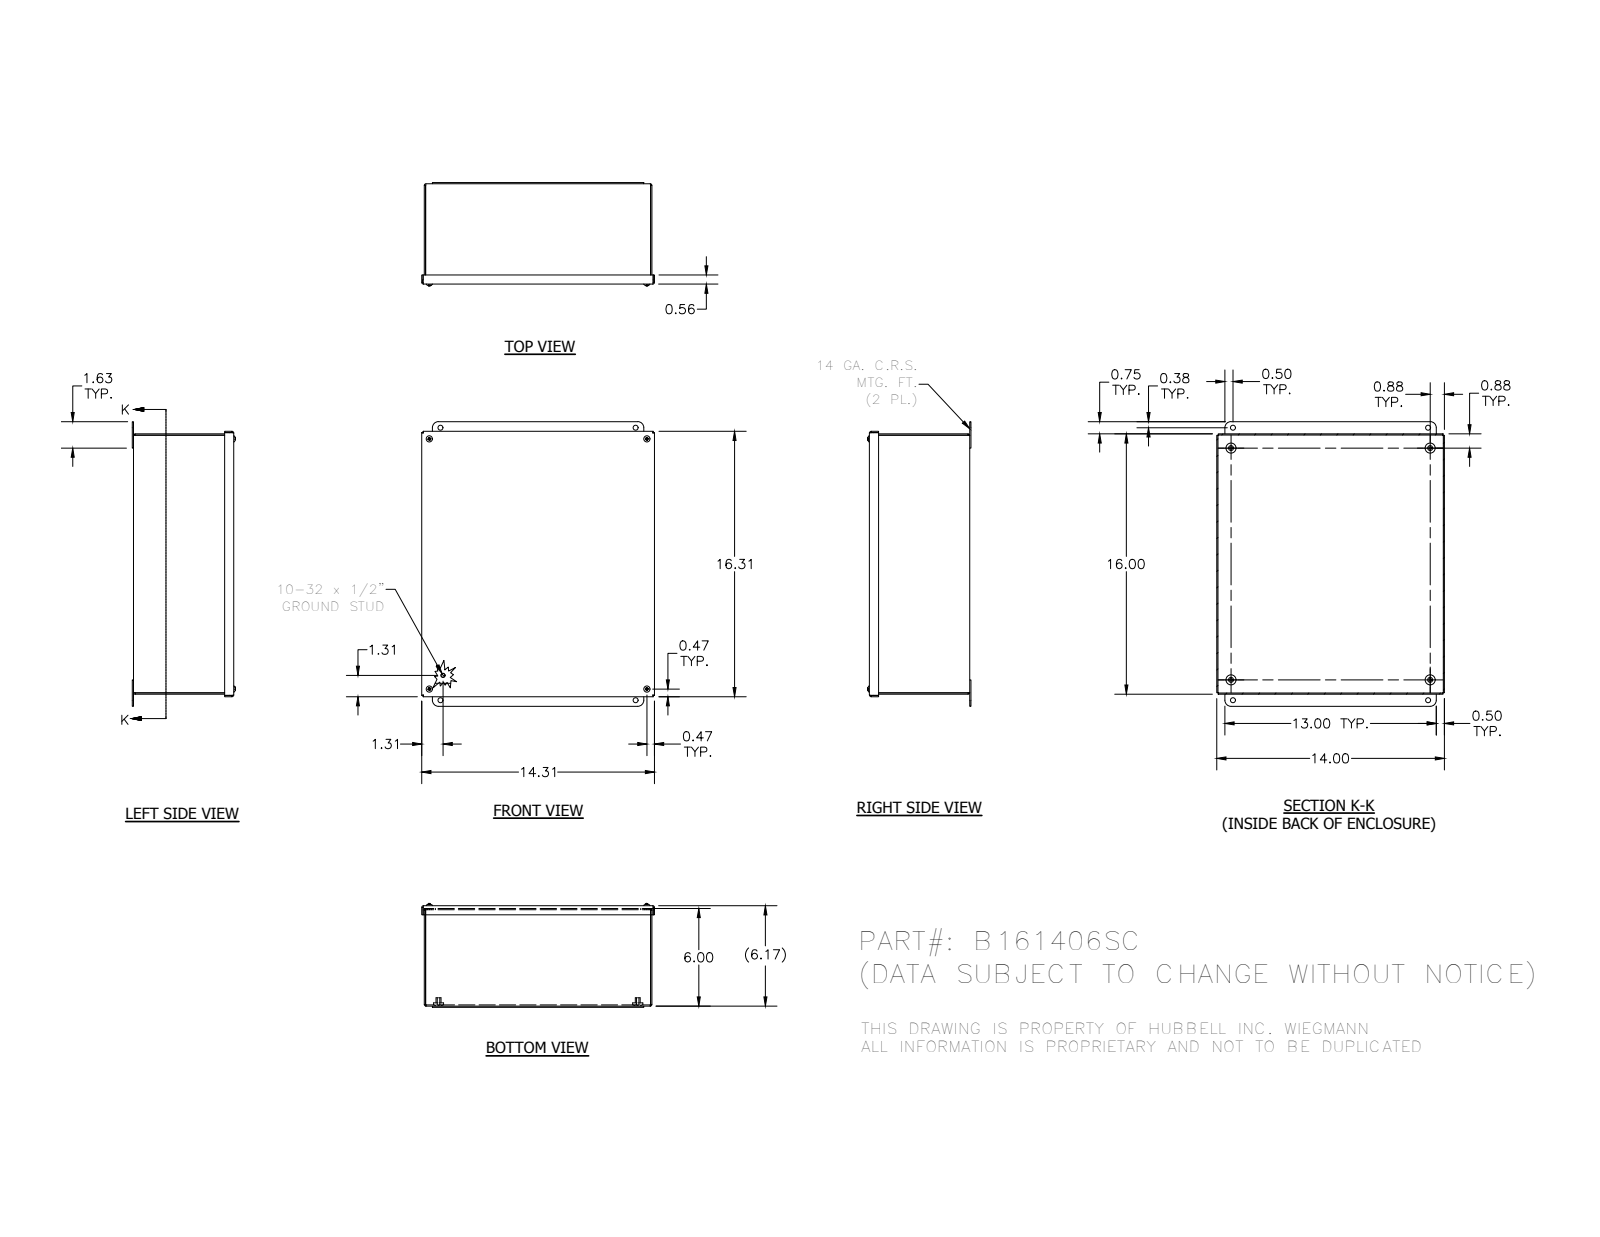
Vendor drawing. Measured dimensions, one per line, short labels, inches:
name: B161406SC; 3486; 34984; B161406SCBKP (+6 more)
written by: Autodesk Inventor 2012 (AUTOMOTIVE_DESIGN)
unit: in
bodies: 23 solids, 532 faces (311 planar, 102 cylindrical, 119 other)
size: 17.5 × 14.313 × 6.346
volume: 74.34 in³; area: 1 920 in²
holes: 4× ⌀0.145, 4× ⌀0.156, 4× ⌀0.196, 4× ⌀0.278, 4× ⌀0.281, 4× ⌀0.31, 4× ⌀0.313
bosses: 5× ⌀0.19, 4× ⌀0.625, 4× ⌀0.453, 4× ⌀0.406, 4× ⌀0.373, 4× ⌀0.3, 4× ⌀0.248, 1× ⌀0.25
rounds: 12× R0.031, 12× R0.105, 4× R0.089, 4× R0.375
face distances: 0.074, 6.094, 6.168, 6.02, 13.926, 15.926, 13.852, 14, 16, 15.852
hole spacings: 0.972, 12.706, 15.395, 16.077, 12.824, 14.823, 20.469, 1.256
